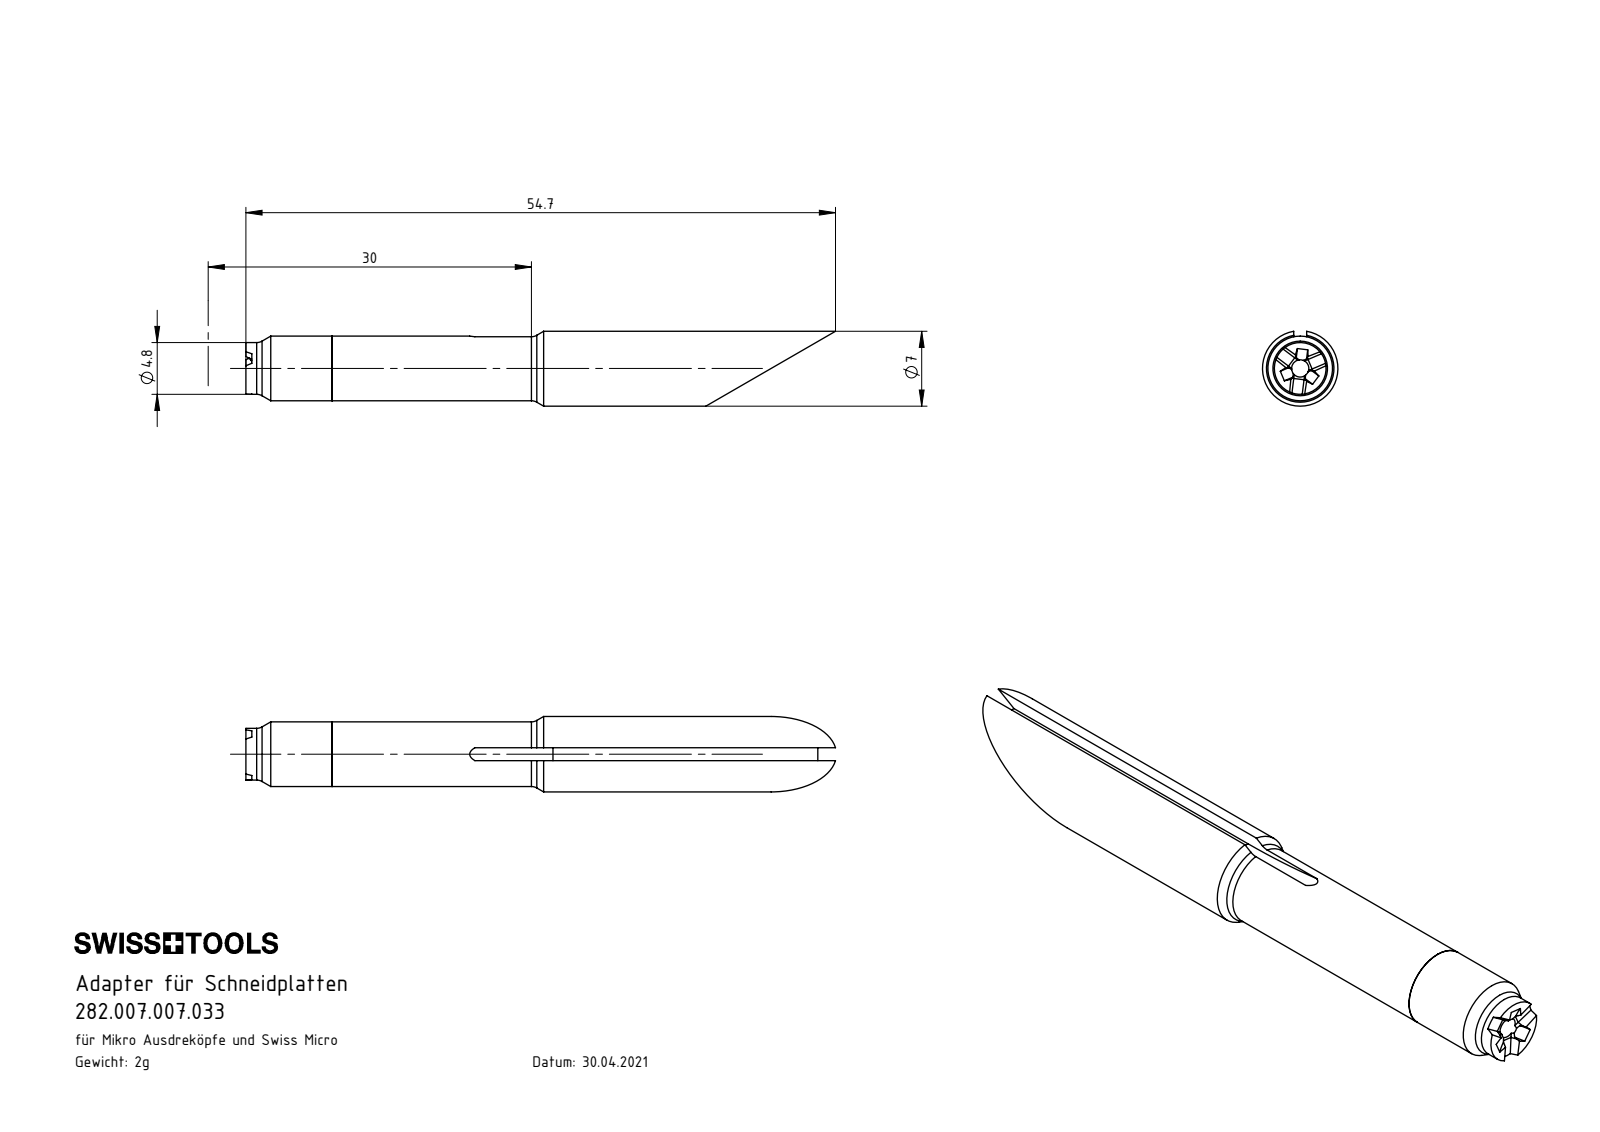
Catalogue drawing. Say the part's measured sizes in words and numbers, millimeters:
The part is named "282.007.007.033". Its 3-D file was written by "SolidWorks 2022 (CONFIG_CONTROL_DESIGN)". It is 1 solid with 89 faces: 17 planar, 43 cylindrical and 29 other. Overall it measures 54.72 by 7 by 6.95 millimeters. Its volume is 1 527 cubic millimeters and its surface area 1 181 square millimeters. Round holes: 1 of diameter 1.6. Round bosses or shafts: 1 of diameter 7, 1 of diameter 6, 1 of diameter 4.8. Partial cylindrical surfaces (rounded edges, fillets, slot ends): 3 of radius 4.9, 1 of radius 60. The main face-to-face distances are 1.2, 2.5.
